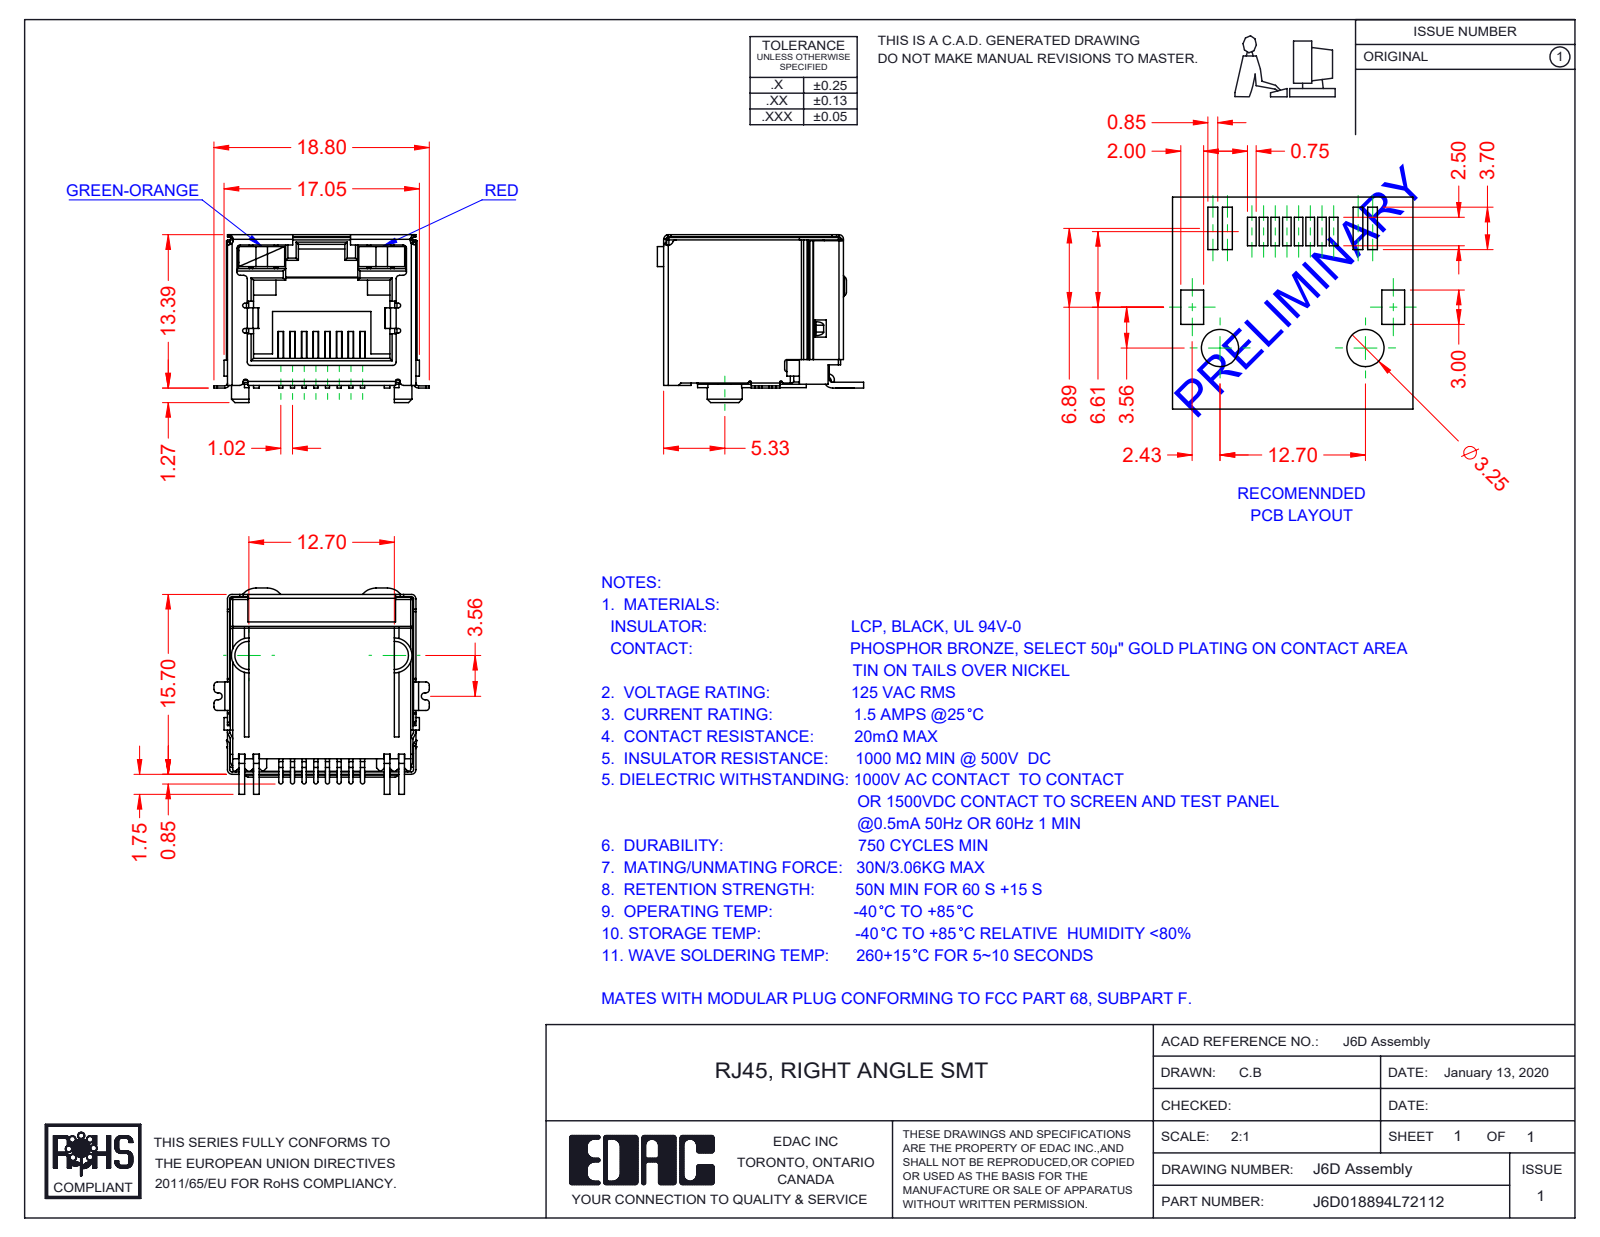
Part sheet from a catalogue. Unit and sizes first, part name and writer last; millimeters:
Units: millimetres
Overall size (bounding box): 18.8 × 18 × 14.65
Partial cylindrical surfaces — rounded edges, fillets, slot ends (radius × count): R0.3 ×39, R0.2 ×37, R0.4 ×16, R0.1 ×12, R0.15 ×8, R0.18 ×8, R0.5 ×6, R1.5 ×5
Main face-to-face distances: 16, 16.25, 16.2, 2.25, 1, 15.95, 16.05, 12.8, 0.45, 16.45
Volume: 1 804 mm³ · Surface area: 4 898 mm²
Bodies: 12 solids, 896 faces (645 planar, 218 cylindrical, 33 other)
Part name (STEP PRODUCT): 6D Contacts; J6D018894L72112; 6D Shield_LED - No EMI; 6D Insulator (+2 more)
STEP written by: SolidWorks 2016 (CONFIG_CONTROL_DESIGN)
